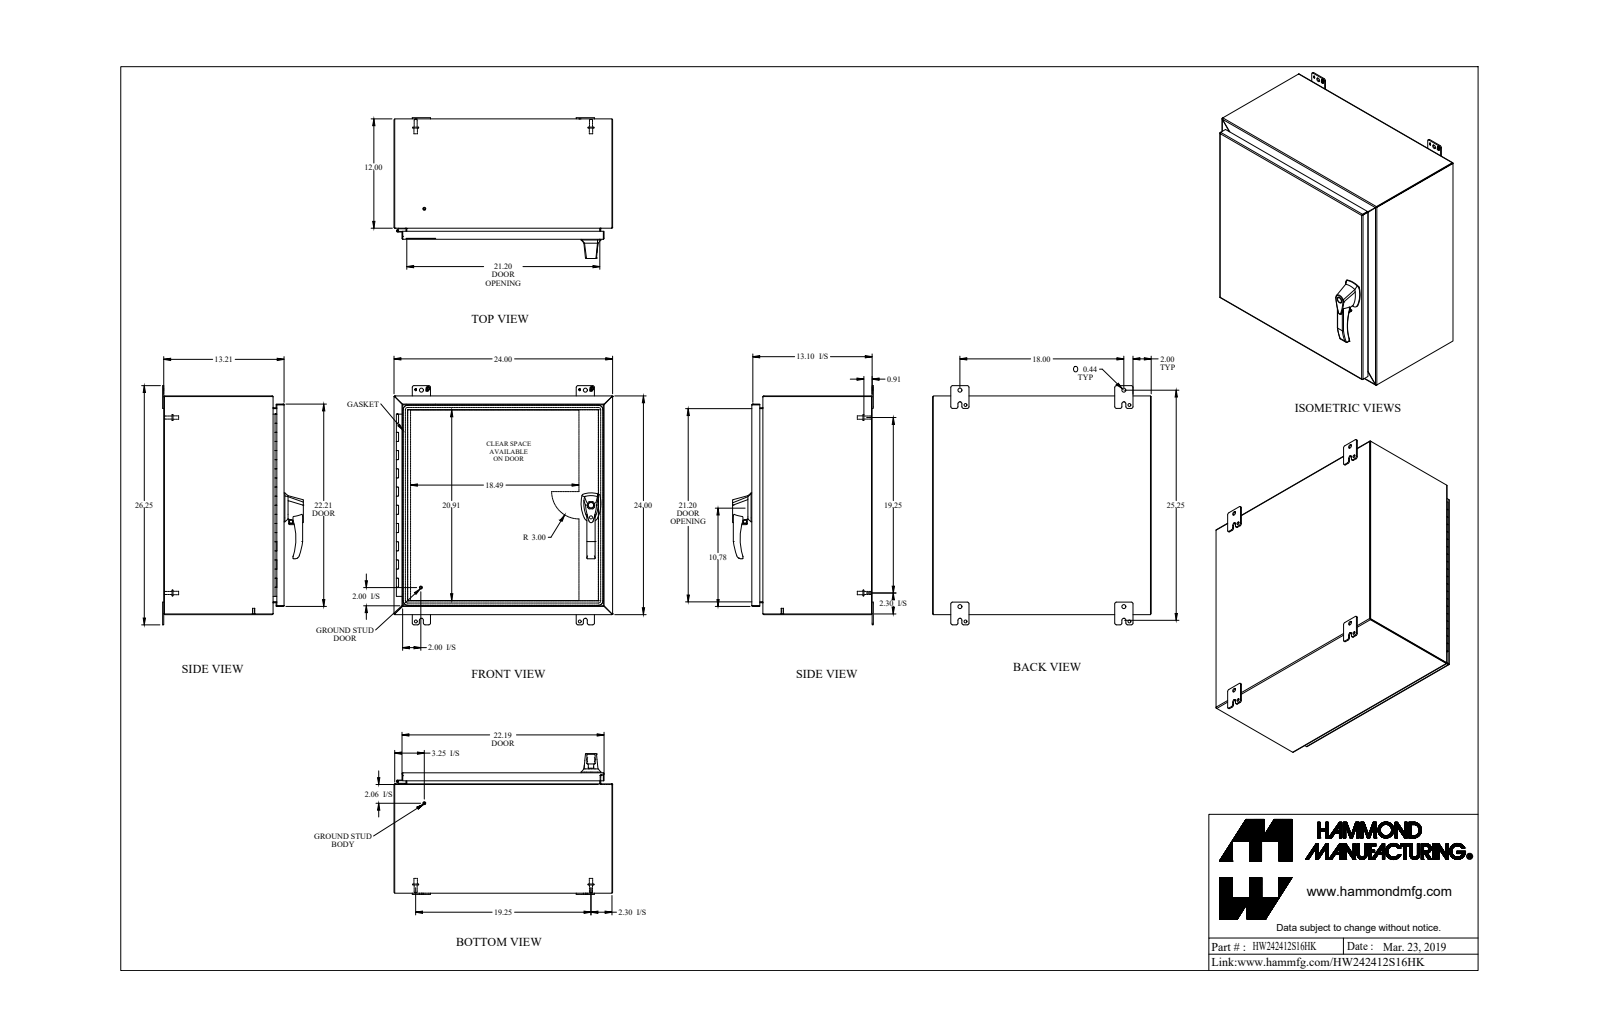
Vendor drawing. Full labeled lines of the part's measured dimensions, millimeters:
Part name (STEP PRODUCT): HW242412S16HK
STEP written by: SolidWorks 2018 (AUTOMOTIVE_DESIGN)
Units: millimetres
Bodies: 44 solids, 1366 faces (654 planar, 568 cylindrical, 144 other)
Overall size (bounding box): 666.8 × 609.6 × 392.4
Volume: 3 517 000 mm³ · Surface area: 3 588 000 mm²
Round holes (diameter × count): ⌀4.5 ×6, ⌀8 ×5, ⌀6.4 ×3, ⌀6.7 ×3, ⌀10.5 ×3, ⌀5 ×2, ⌀6.5 ×2, ⌀10 ×2, ⌀11.1 ×2, ⌀2.8 ×1, ⌀5.9 ×1, ⌀8.4 ×1
Round bosses / shafts (diameter × count): ⌀9.5 ×9, ⌀6.4 ×7, ⌀4 ×6, ⌀16.5 ×4, ⌀8.4 ×4, ⌀25.4 ×3, ⌀13 ×3, ⌀8 ×3
Partial cylindrical surfaces — rounded edges, fillets, slot ends (radius × count): R6.4 ×27, R4.8 ×24, R0.9 ×18, R2.7 ×18, R1.5 ×12, R3.2 ×9, R1.1 ×8, R5.5 ×8
Main face-to-face distances: 1.8, 607.8, 1.8, 605.9, 609.6, 333.7, 331.9, 333.7, 335.5, 303
Hole centre spacings: 206.2, 206.2, 412.4, 28.2, 34, 172.2, 192.4, 192.5
